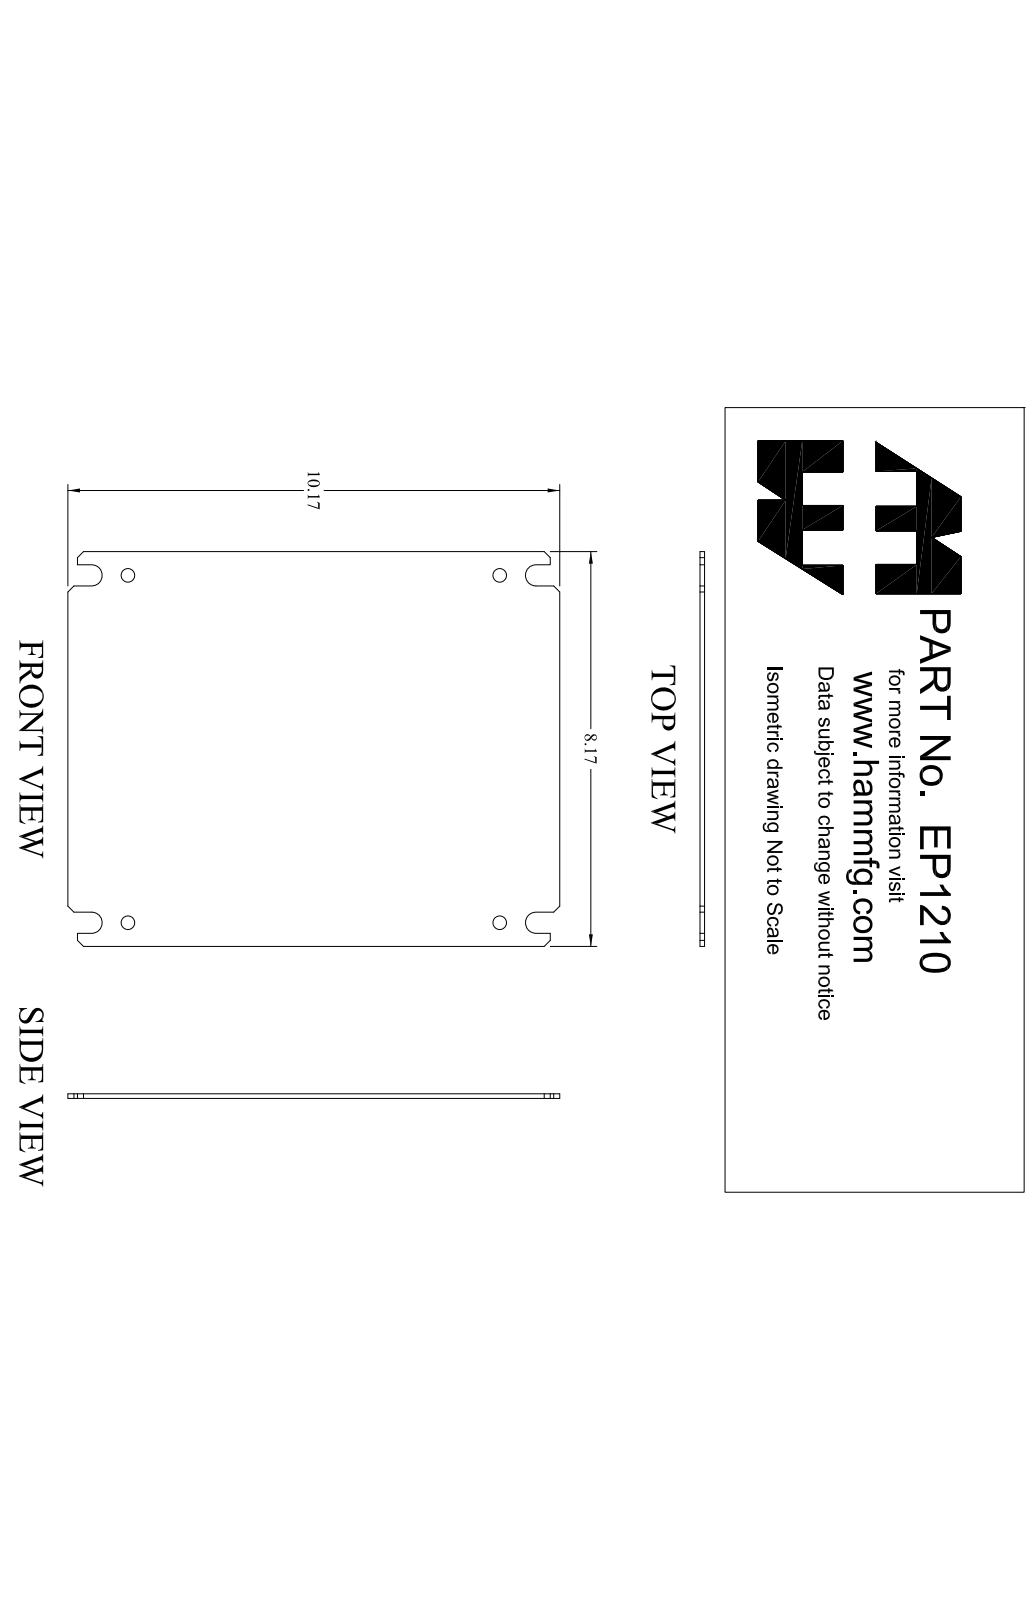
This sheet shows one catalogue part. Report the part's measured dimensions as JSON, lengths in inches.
{"part_name": "EP1210", "step_written_by": "SolidWorks 2018 (AUTOMOTIVE_DESIGN)", "units": "inches", "bodies": {"solids": 1, "faces": 40, "planar": 26, "cylindrical": 14, "other": 0}, "overall_size": [10.17, 8.17, 0.095], "volume_in3": 7.734, "surface_area_in2": 166.9, "round_holes": [[0.281, 4]], "partial_cylinders_radius": [[0.219, 4]], "face_to_face_distances": [0.095, 8.17, 10.17, 0.709, 7.461, 0.272, 7.898, 0.437, 7.188, 6.751], "hole_center_spacings": [7.188, 7.688, 10.525]}
